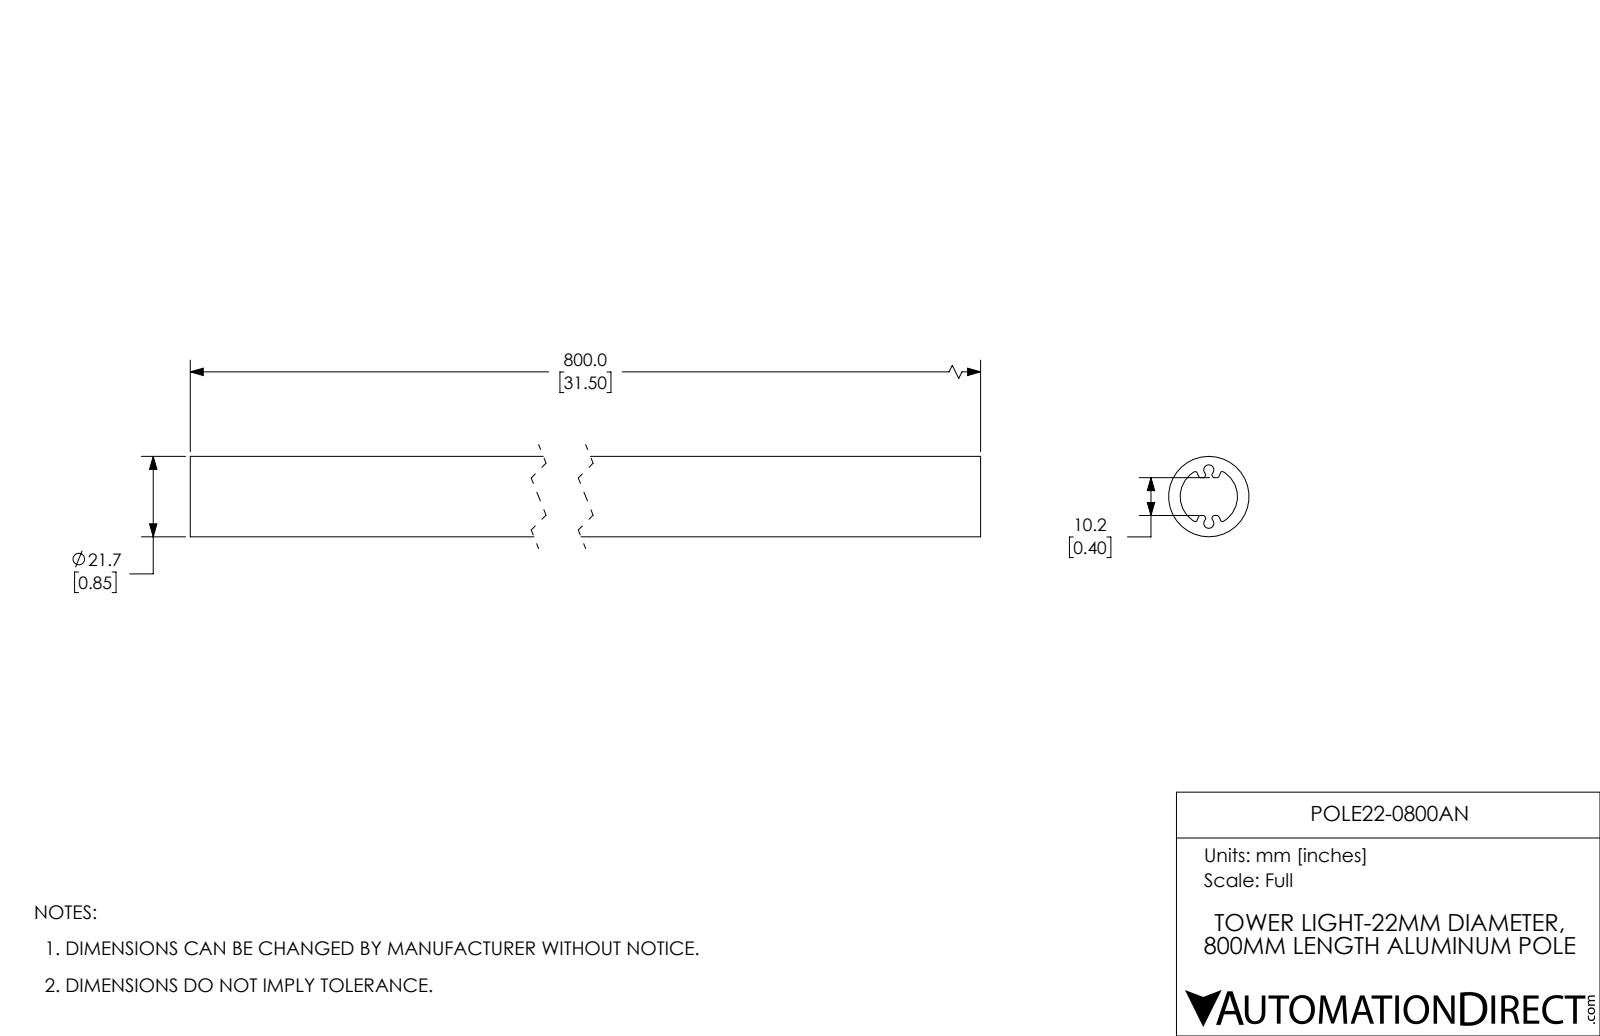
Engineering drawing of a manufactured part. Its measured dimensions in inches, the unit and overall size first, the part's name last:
Units: inches
Overall size (bounding box): 31.496 × 0.854 × 0.854
Round bosses / shafts (diameter × count): ⌀0.854 ×1
Main face-to-face distances: 31.496
Volume: 9.556 in³ · Surface area: 165.3 in²
Bodies: 1 solid, 8 faces (2 planar, 2 cylindrical, 4 other)
Part name (STEP PRODUCT): POLE22-0800AN
STEP written by: SolidWorks 2017 (AUTOMOTIVE_DESIGN)
